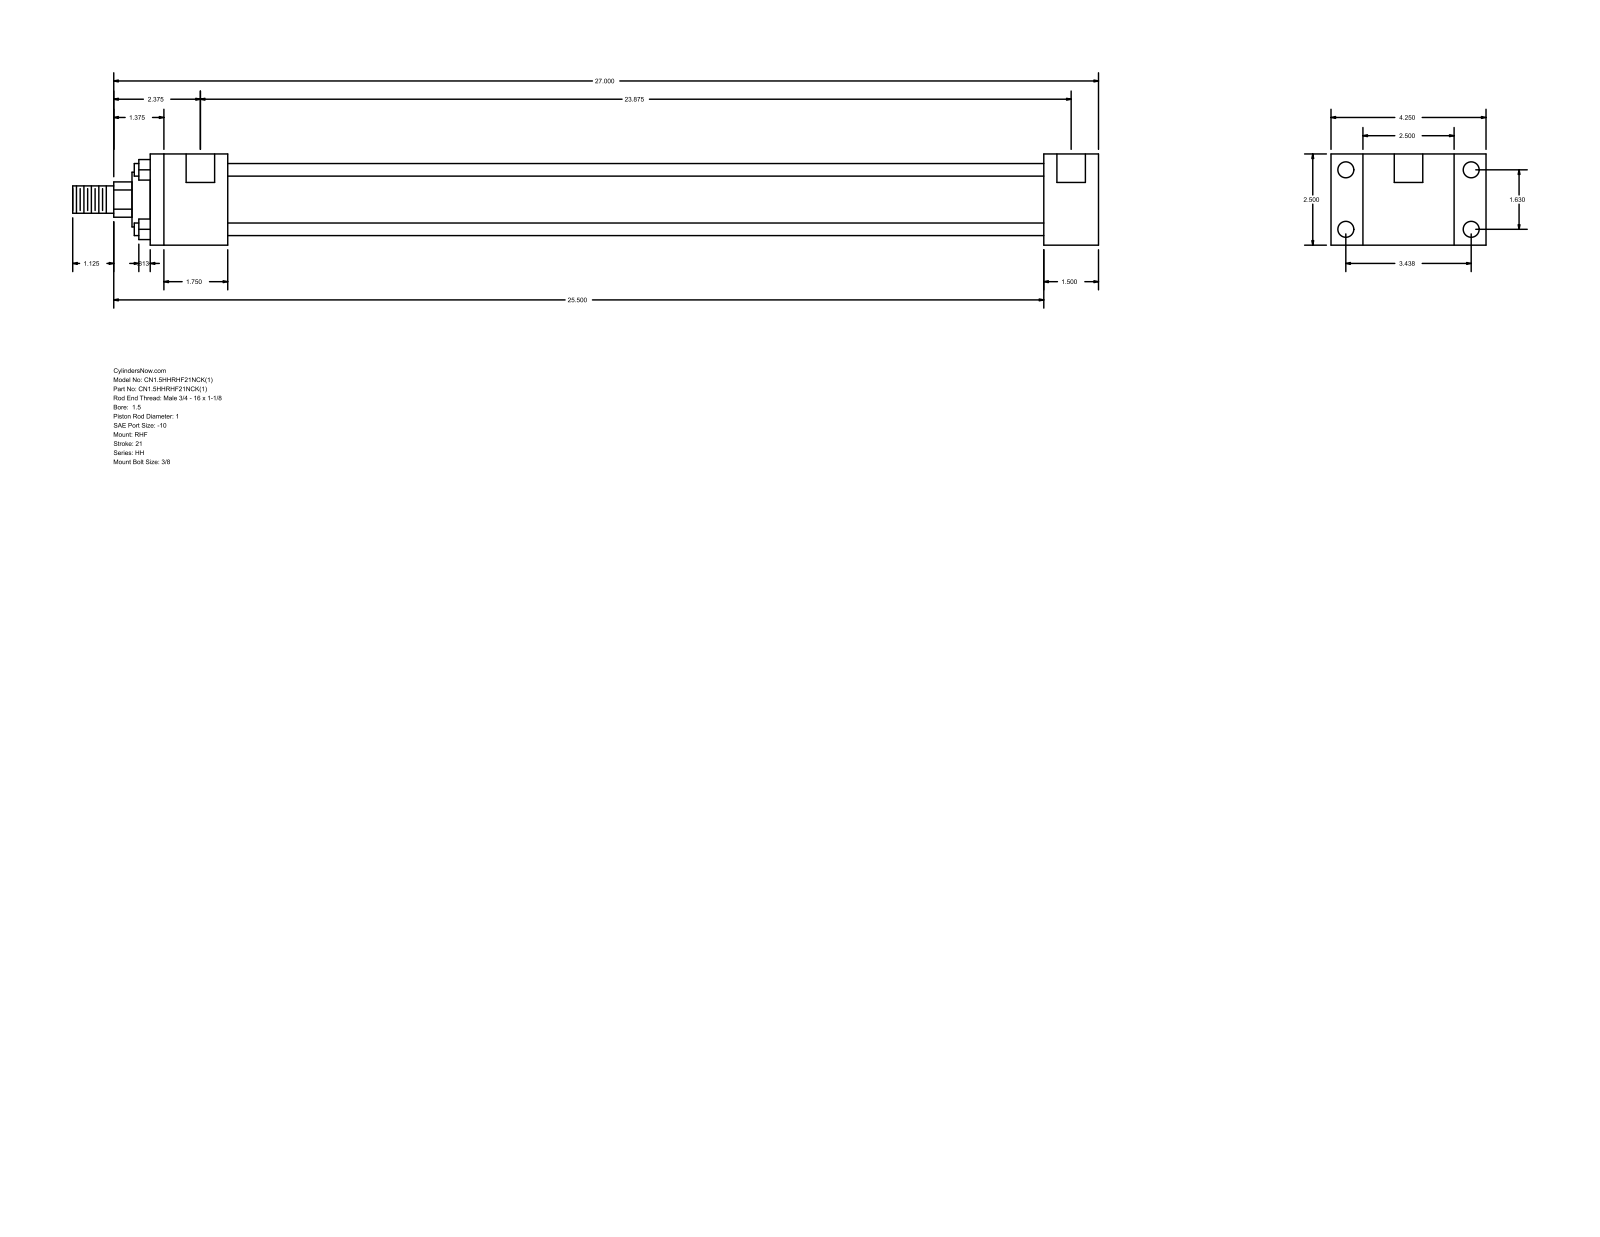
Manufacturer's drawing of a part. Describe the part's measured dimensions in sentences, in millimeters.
The part is named "HH_RHF__0150_1". Its 3-D file was written by "GSSL Pune (CONFIG_CONTROL_DESIGN)". It is 0 solids with 88 faces: 60 planar, 28 cylindrical and 0 other. Overall it measures 714.38 by 107.95 by 63.5 millimeters. Round holes: 4 of diameter 5.56, 4 of diameter 11.13, 2 of diameter 19.84. Round bosses or shafts: 4 of diameter 8.76, 1 of diameter 44.45, 1 of diameter 38.1, 1 of diameter 25.4, 1 of diameter 19.05. Partial cylindrical surfaces (rounded edges, fillets, slot ends): 1 of radius 12.29. The main face-to-face distances are 63.5, 22.23, 85.73, 38.1, 107.96, 568.32, 606.42, 53.98, 622.3, 660.4. The hole center spacings are 1.59, 41.4, 87.32, 96.64, 608.01, 609.6, 606.42.
